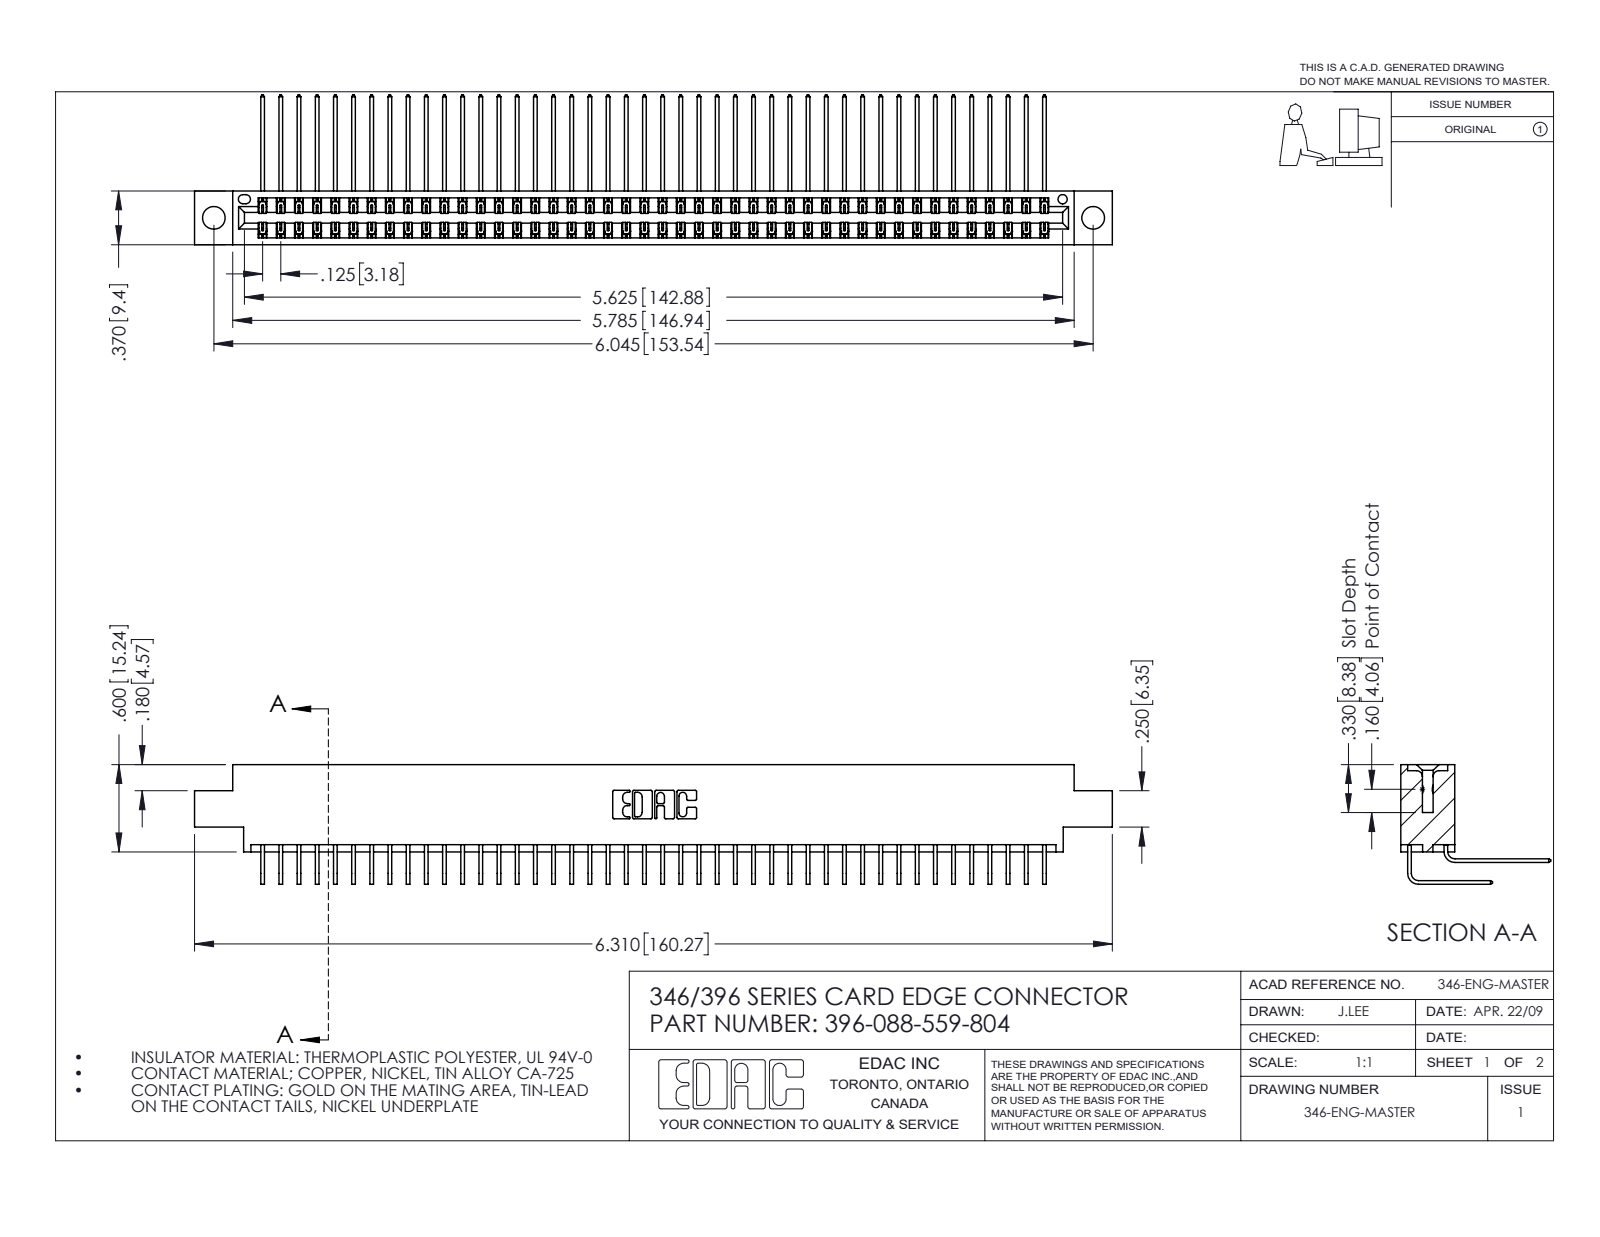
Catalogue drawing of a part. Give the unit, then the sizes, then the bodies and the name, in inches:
Units: inches
Overall size (bounding box): 6.31 × 1.03 × 0.823
Round holes (diameter × count): ⌀0.156 ×2, ⌀0.064 ×1
Partial cylindrical surfaces — rounded edges, fillets, slot ends (radius × count): R0.006 ×132, R0.01 ×22, R0.007 ×6, R0.031 ×6, R0.026 ×3, R0.014 ×2, R0.022 ×2, R0.024 ×2
Main face-to-face distances: 0.048, 0.322, 0.025, 0.37, 0.25, 0.072, 0.298, 0.275, 0.148, 0.222
Hole centre spacings: 0.246, 5.836, 6.045
Volume: 0.971 in³ · Surface area: 37.71 in²
Bodies: 89 solids, 4878 faces (3336 planar, 1542 cylindrical, 0 other)
Part name (STEP PRODUCT): 396-088-559-804; 345-292-001_559 Tail - 2; 345-292-001_558 559 Tail - 1; 346 Part_0.170 Offset - 0.156 Dia-TH
STEP written by: SolidWorks 2016 (CONFIG_CONTROL_DESIGN)
